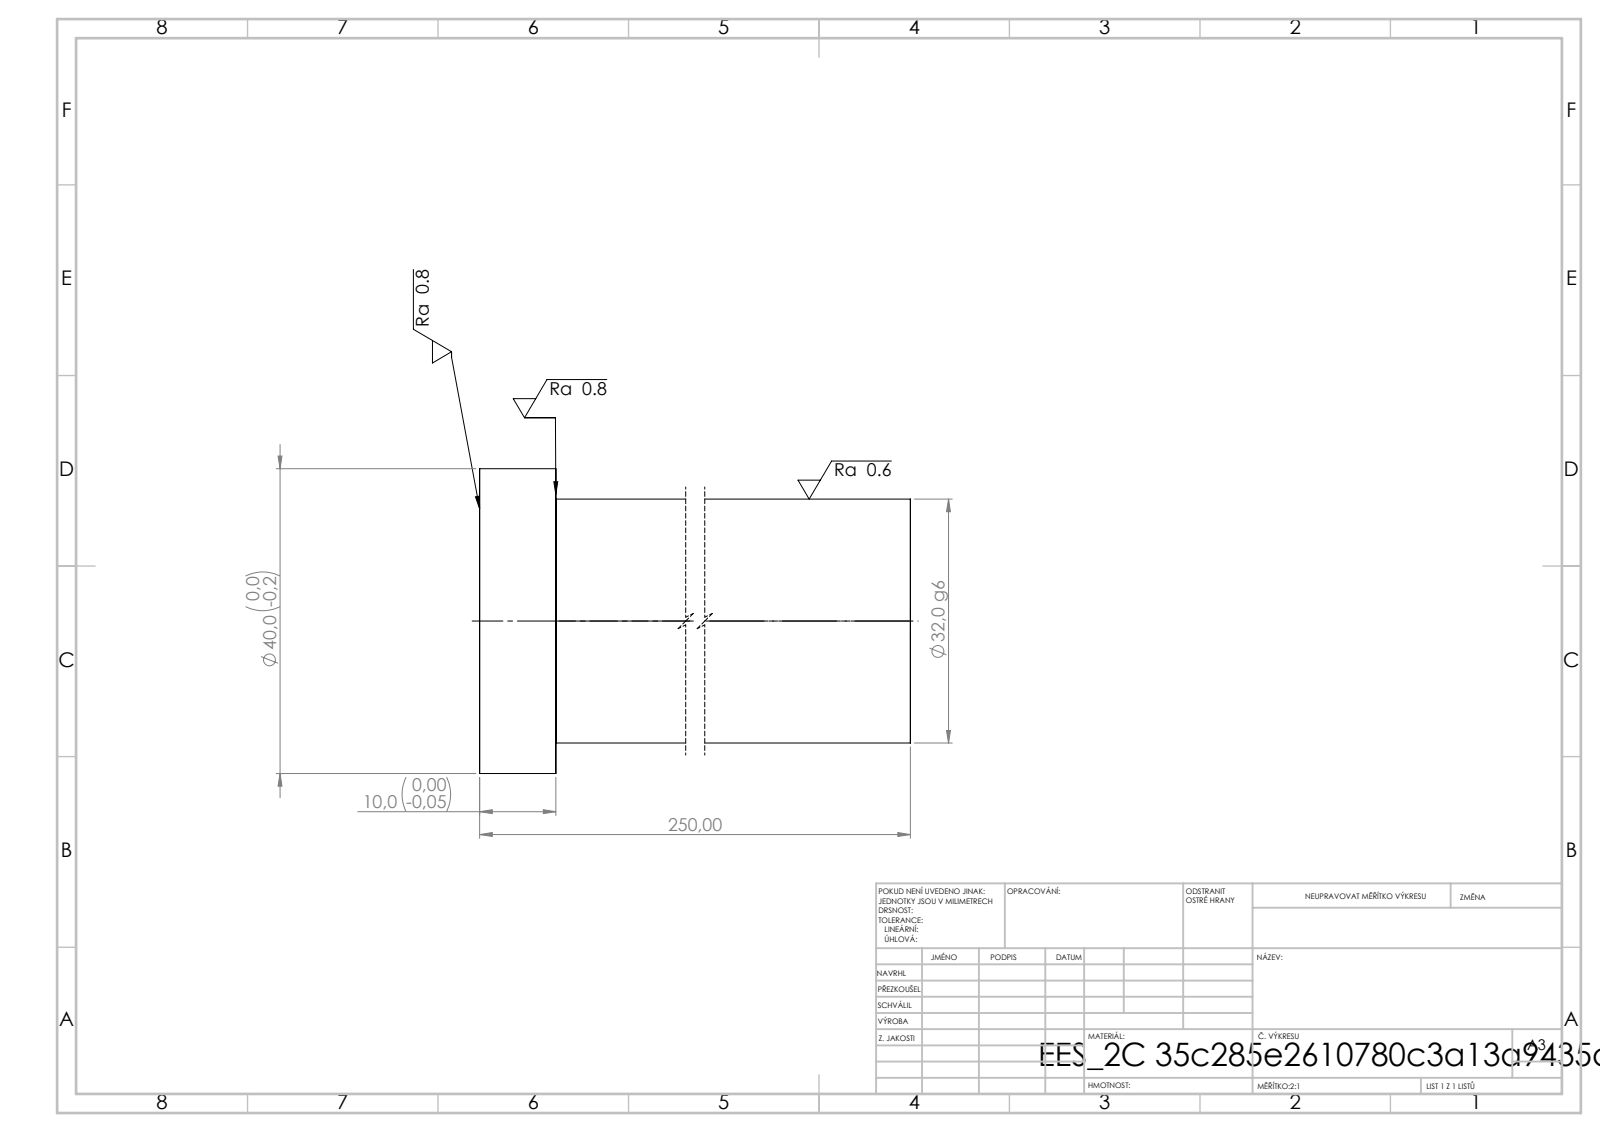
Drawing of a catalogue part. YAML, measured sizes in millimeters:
step_written_by: "SolidWorks 2019 (CONFIG_CONTROL_DESIGN)"
units: millimeters
bodies: {solids: 1, faces: 7, planar: 3, cylindrical: 4, other: 0}
overall_size: [250, 40, 40]
volume: 205586
surface_area: 27897
round_bosses_or_shafts:
  - {diameter: 40, count: 1}
  - {diameter: 32, count: 1}
face_to_face_distances: [250, 10, 240]
